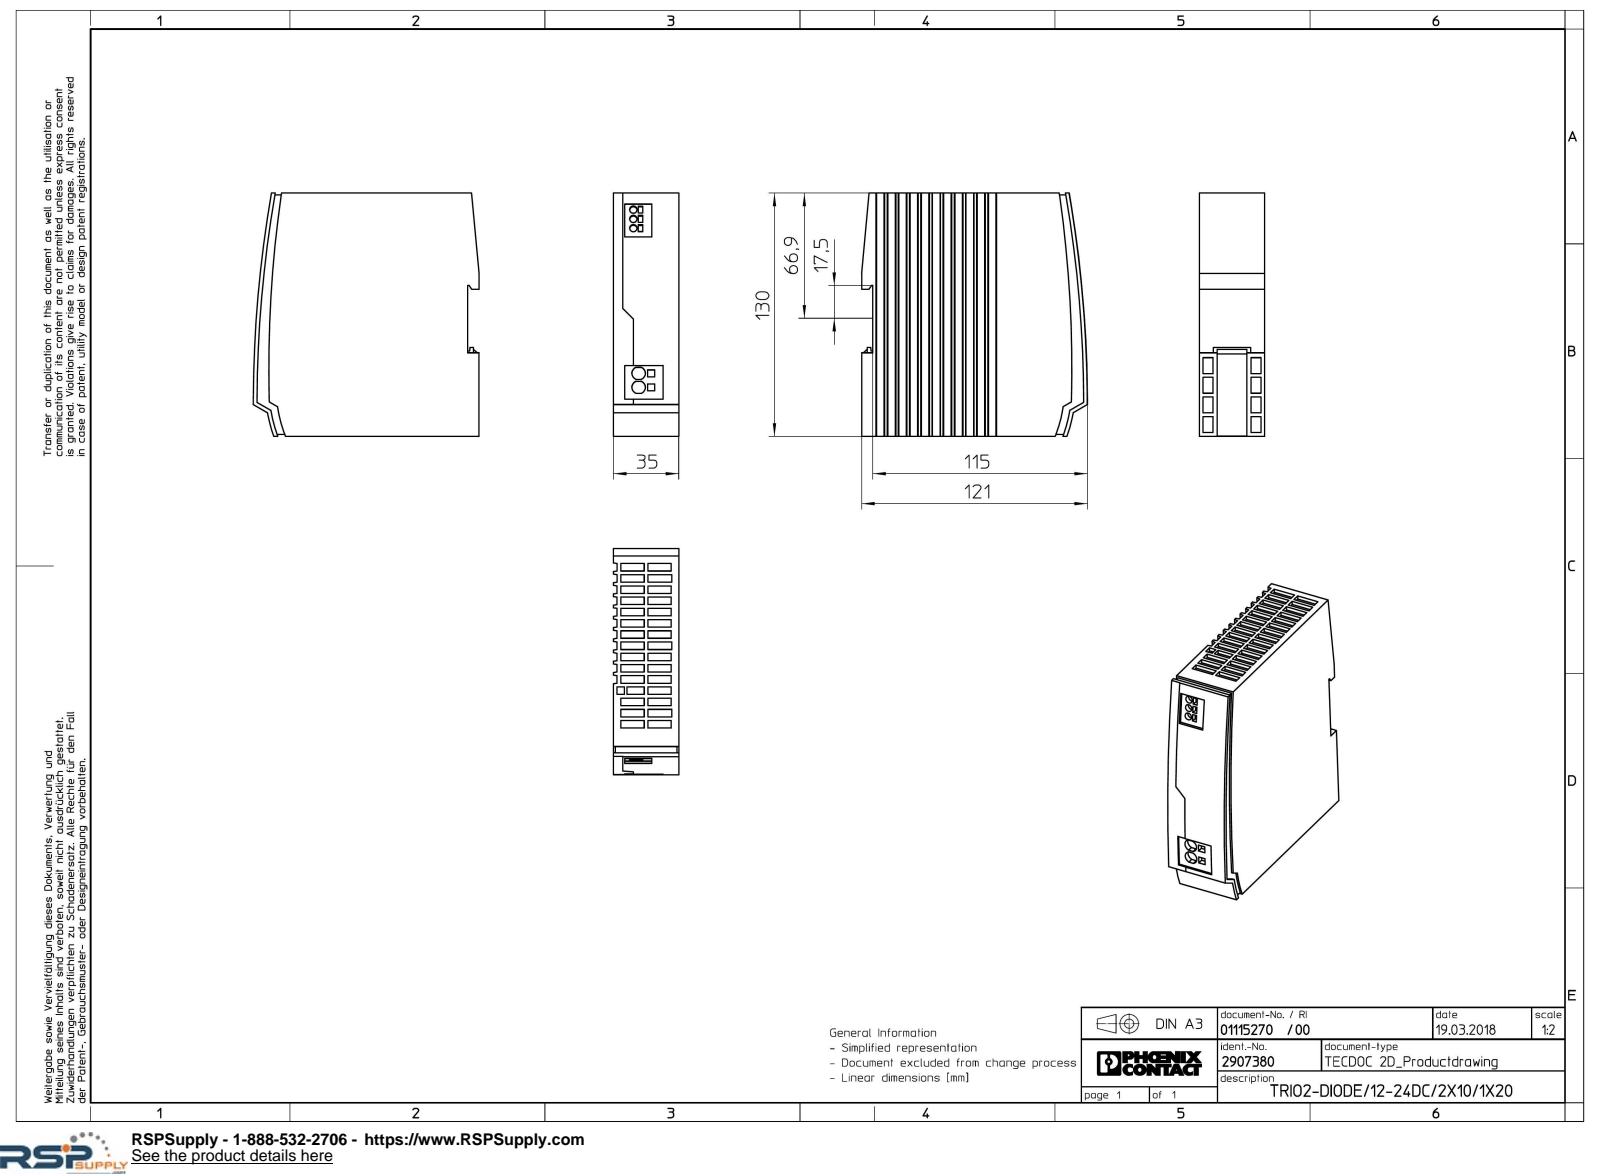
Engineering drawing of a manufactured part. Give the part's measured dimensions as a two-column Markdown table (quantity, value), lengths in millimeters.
| quantity | value |
| --- | --- |
| part name | TRIO2_DIODE_12_24DC_2X10_1X20-select |
| STEP written by | Creo Elements/Direct Modeling 18.1I 14-Aug-2016 (C) Parametric Technology GmbH (AUTOMOTIVE_DESIGN) |
| units | millimeters |
| bodies | 1 solid, 510 faces (493 planar, 17 cylindrical, 0 other) |
| overall size | 130 × 121 × 35 |
| volume | 500 853 mm³ |
| surface area | 58 008 mm² |
| round holes (diameter × count) | 4 × 3 |
| partial cylindrical surfaces (radius × count) | 3.45 × 4, 69.15 × 1, 73 × 1, 75 × 1, 655.63 × 1, 658 × 1, 659.9 × 1, 660 × 1 |
| main face-to-face distances | 2, 35, 33, 11.87, 17.8, 5.93, 29.67, 128, 1, 23.74 |
| hole center spacings | 5, 10 |
